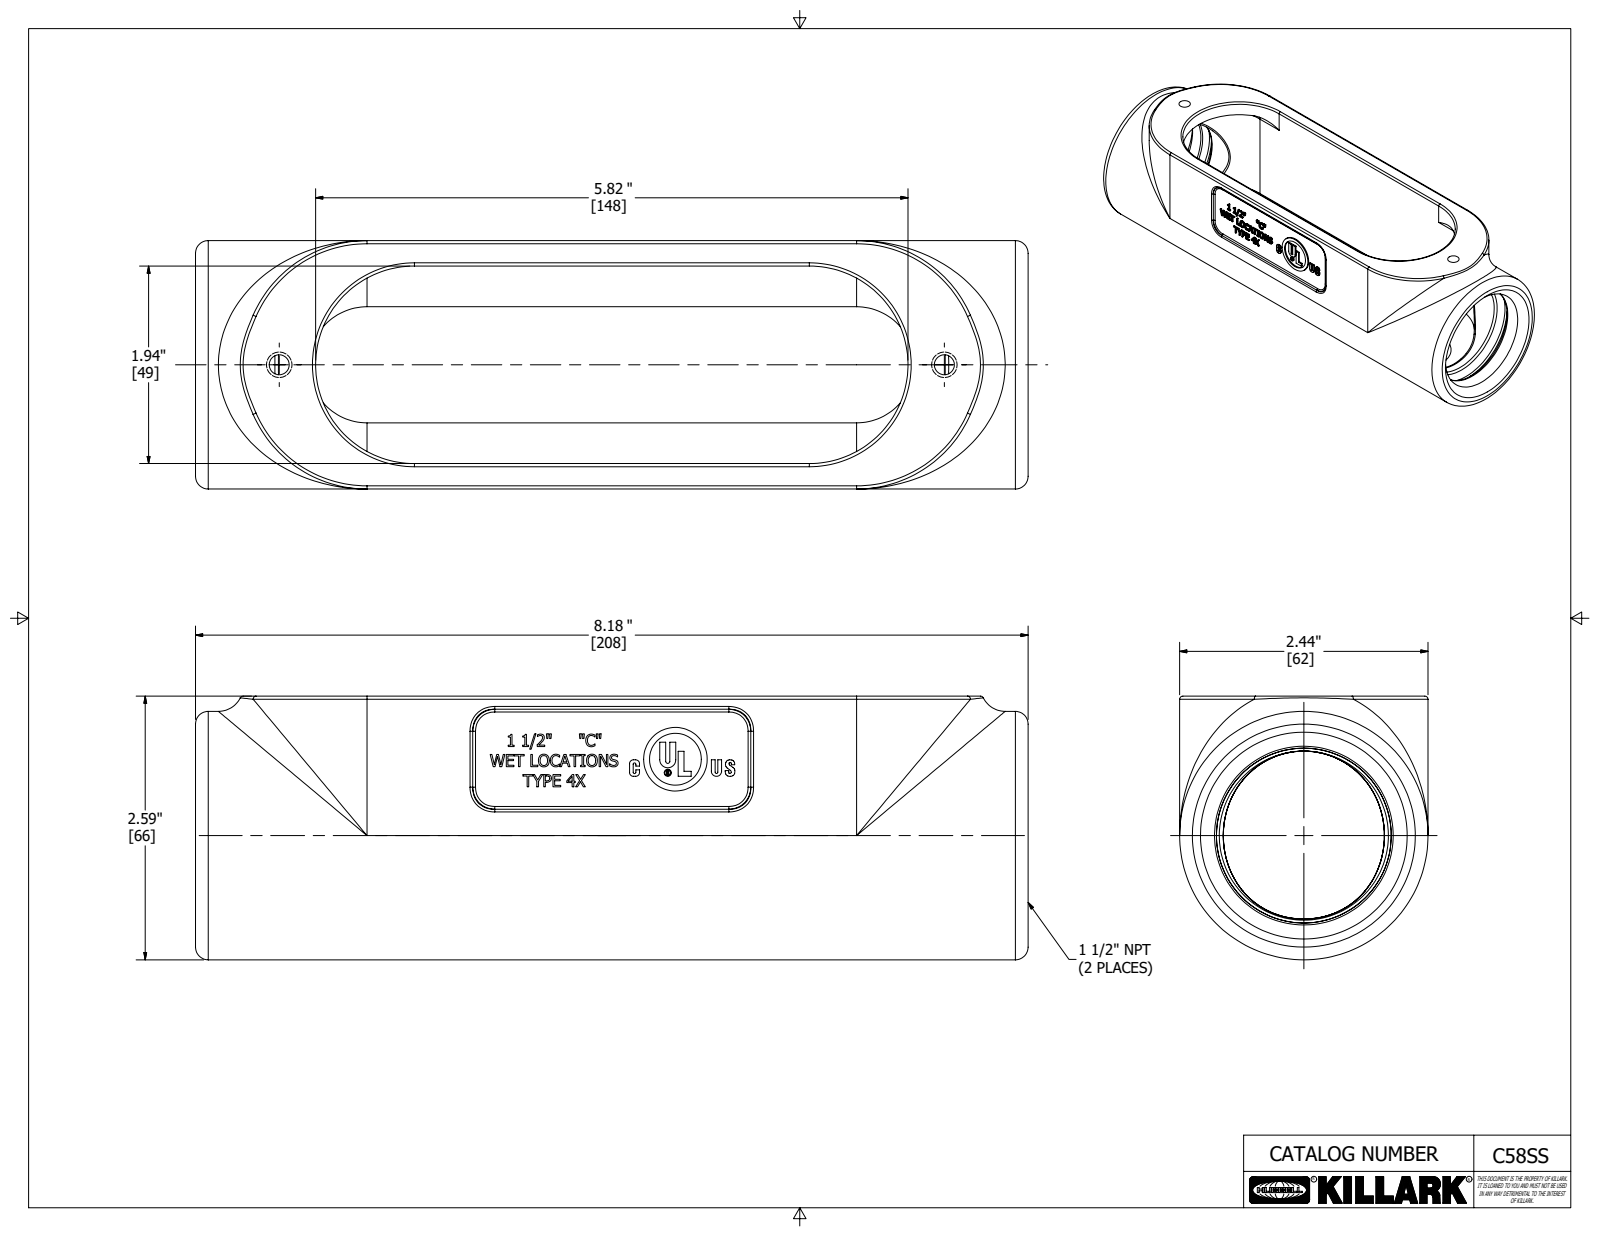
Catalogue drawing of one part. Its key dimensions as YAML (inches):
part_name: "C48SS"
step_written_by: "Autodesk Inventor 2020 (AUTOMOTIVE_DESIGN)"
units: inches
bodies: {solids: 1, faces: 533, planar: 310, cylindrical: 80, other: 143}
overall_size: [8.18, 2.59, 2.44]
volume: 12.74
surface_area: 118.6
round_holes:
  - {diameter: 0.196, count: 2}
  - {diameter: 0.058, count: 1}
  - {diameter: 0.509, count: 1}
  - {diameter: 1.906, count: 1}
round_bosses_or_shafts:
  - {diameter: 2.44, count: 1}
  - {diameter: 0.625, count: 1}
  - {diameter: 0.069, count: 1}
partial_cylinders:
  - {radius: 0.031, count: 13}
  - {radius: 0.038, count: 4}
  - {radius: 0.25, count: 4}
  - {radius: 0.97, count: 4}
  - {radius: 0.013, count: 2}
  - {radius: 0.013, count: 2}
  - {radius: 0.125, count: 2}
  - {radius: 0.4, count: 2}
face_to_face_distances: [0.25, 2.19, 1.94, 2.34, 2.44, 0.219, 0.031, 2.159, 2.409, 2.09]
hole_center_spacings: [0.153, 6.535]
